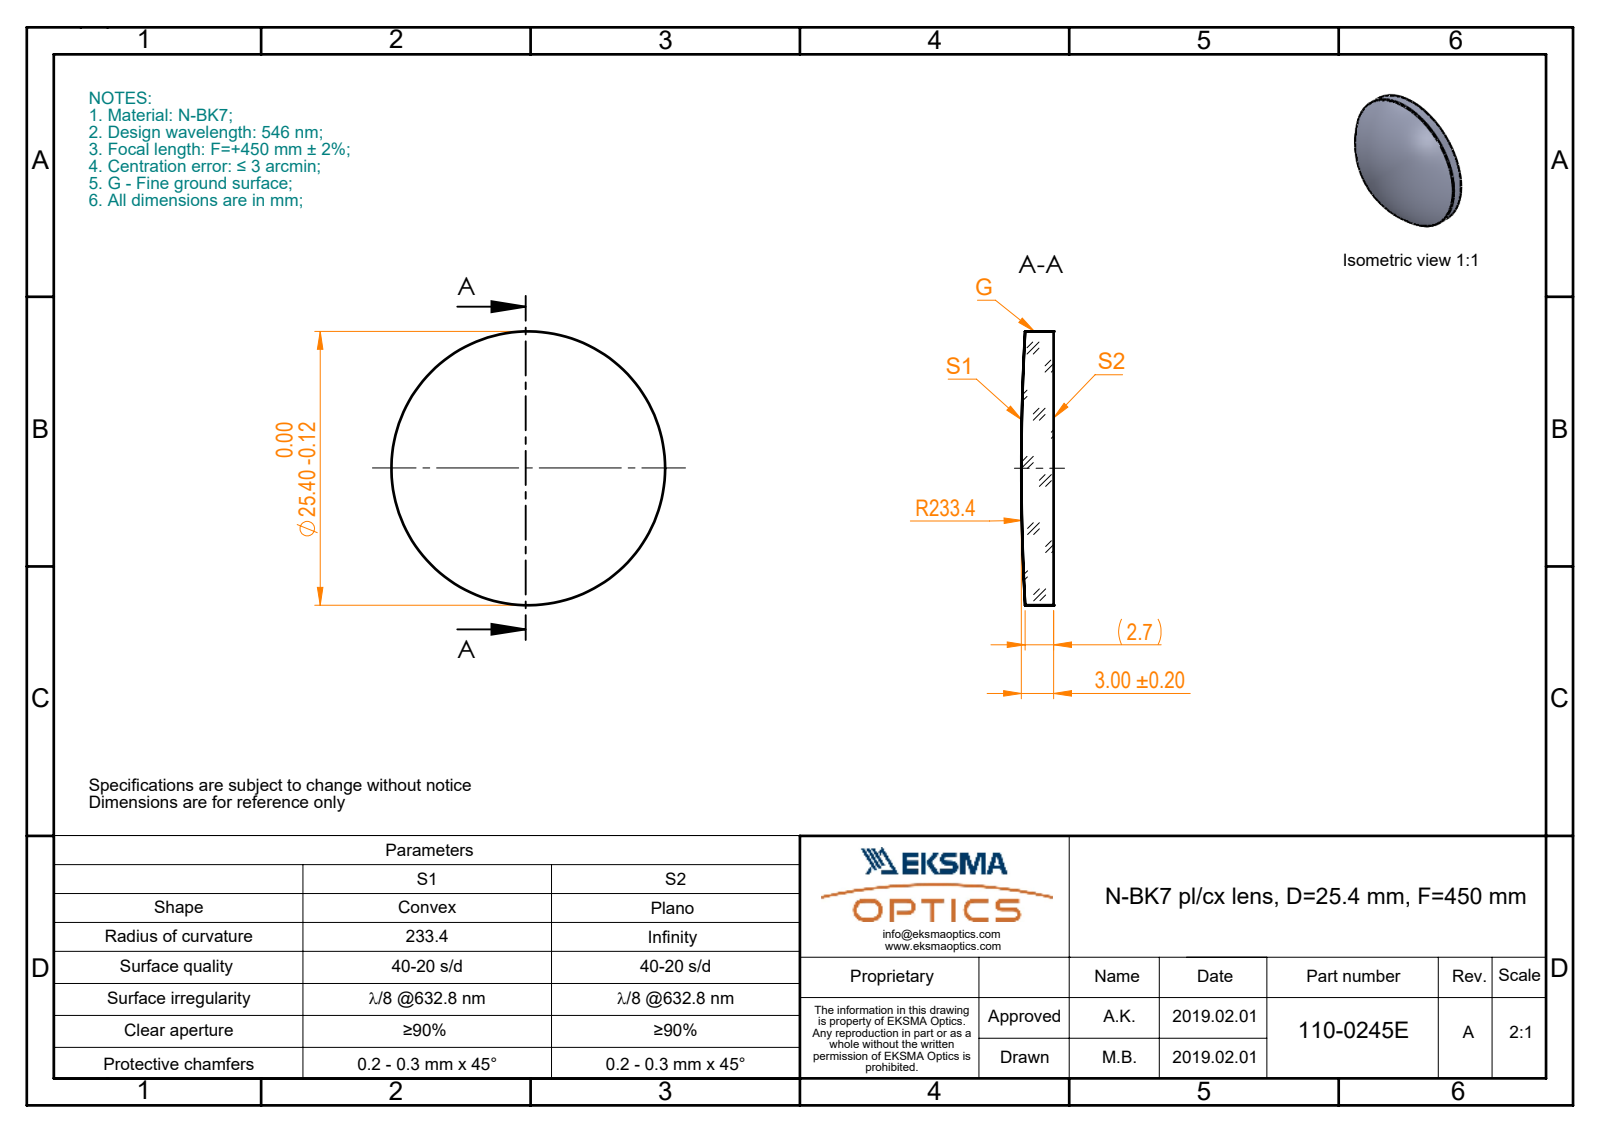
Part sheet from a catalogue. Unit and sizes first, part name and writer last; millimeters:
Units: millimetres
Overall size (bounding box): 25.4 × 25.4 × 3
Round bosses / shafts (diameter × count): ⌀25.4 ×1
Volume: 1 433 mm³ · Surface area: 1 226 mm²
Bodies: 1 solid, 5 faces (1 planar, 2 cylindrical, 2 other)
Part name (STEP PRODUCT): 110-0245E BK7 pl-cx 25.4 F450
STEP written by: SolidWorks 2017 (CONFIG_CONTROL_DESIGN)
